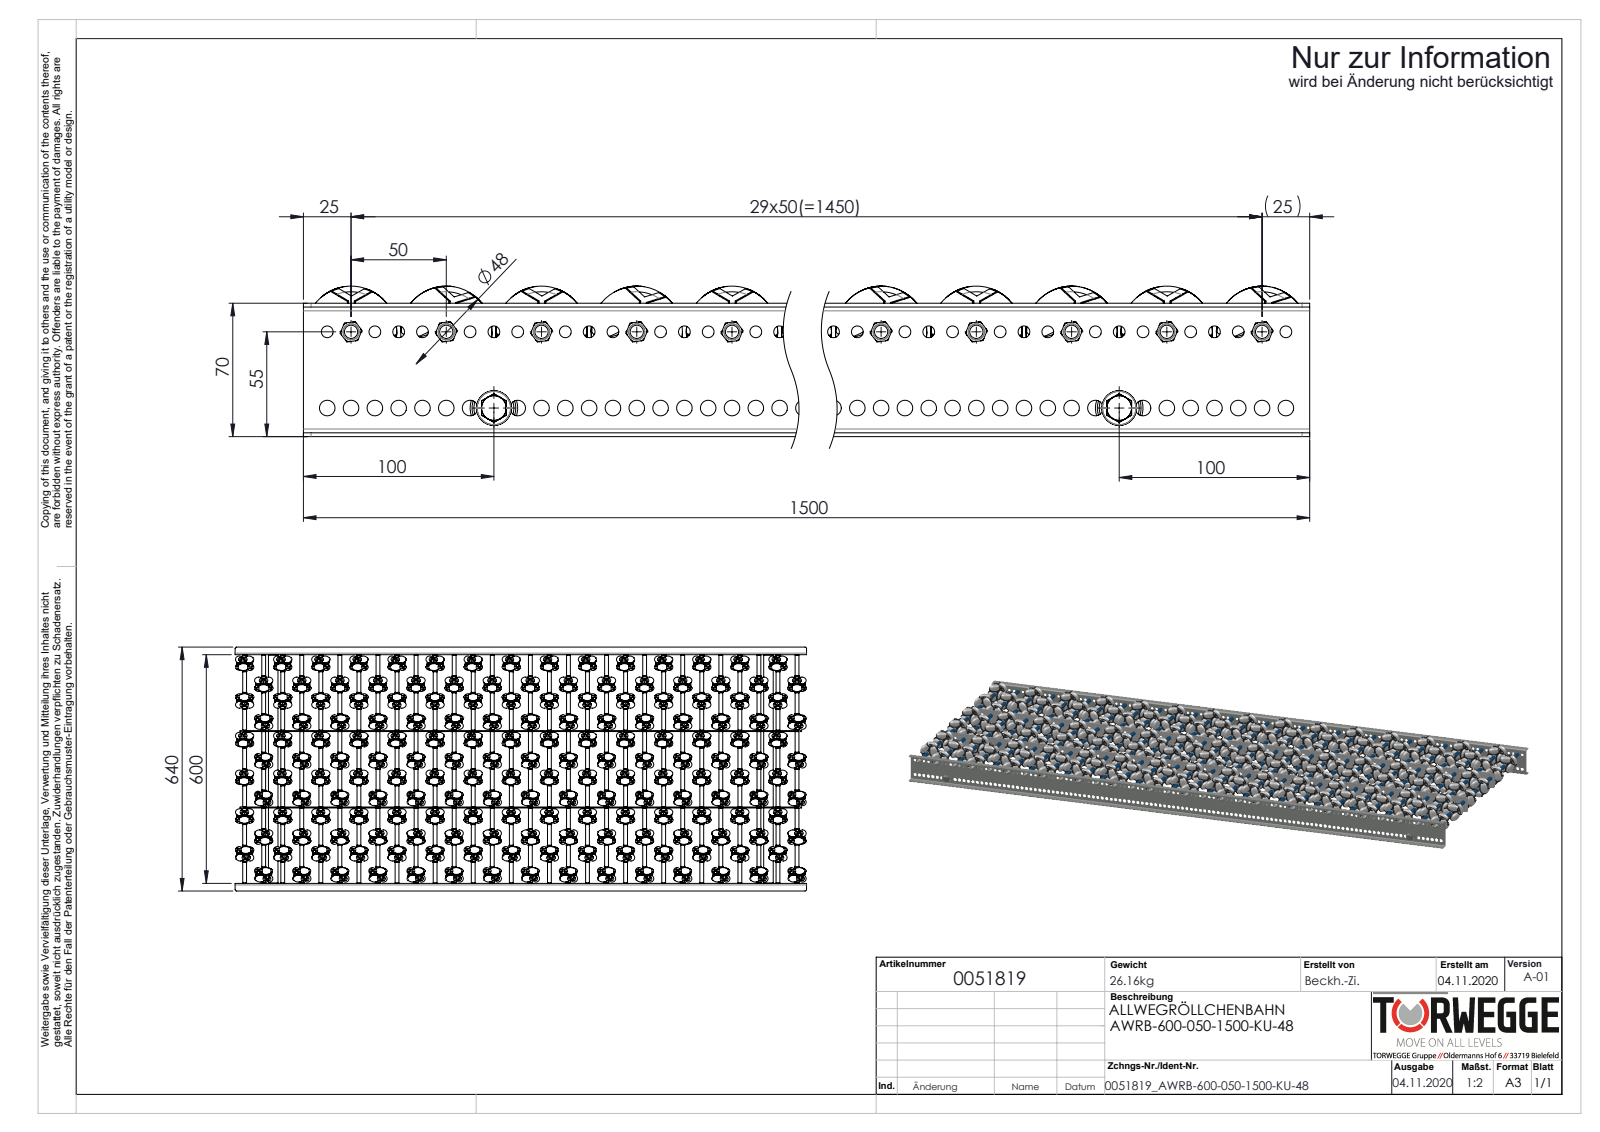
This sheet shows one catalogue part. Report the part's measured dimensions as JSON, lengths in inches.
{"part_name": "0051819; S108767_Längstraverse-42x2,5-AWR_L1500; AWR48_Röllchen; AWR-Achse-für-Konfiguration_L600 (+8 more)", "step_written_by": "SolidWorks 2020 (AUTOMOTIVE_DESIGN)", "units": "inches", "bodies": {"solids": 2984, "faces": 52428, "planar": 18312, "cylindrical": 20272, "other": 13844}, "overall_size": [59.055, 25.197, 3.11], "volume_in3": 592.9, "surface_area_in2": 10070, "round_holes": [[0.146, 1080], [0.165, 1080], [0.244, 119], [0.323, 119], [0.256, 59], [0.194, 30], [0.331, 30], [0.268, 2], [0.827, 2]], "round_bosses_or_shafts": [[0.157, 1080], [0.146, 937], [0.315, 32], [1.854, 30], [1.654, 30], [0.433, 30], [0.394, 30], [0.276, 30]], "partial_cylinders_radius": [[0.157, 8], [0.079, 4], [0.197, 4]], "face_to_face_distances": [0.079, 23.701, 7.894, 0.098, 2.677, 23.622, 23.78, 15.732, 7.795, 7.992], "hole_center_spacings": [1.419, 1.42, 1.42, 1.419, 3.432, 0.122, 0.881, 0.157]}
